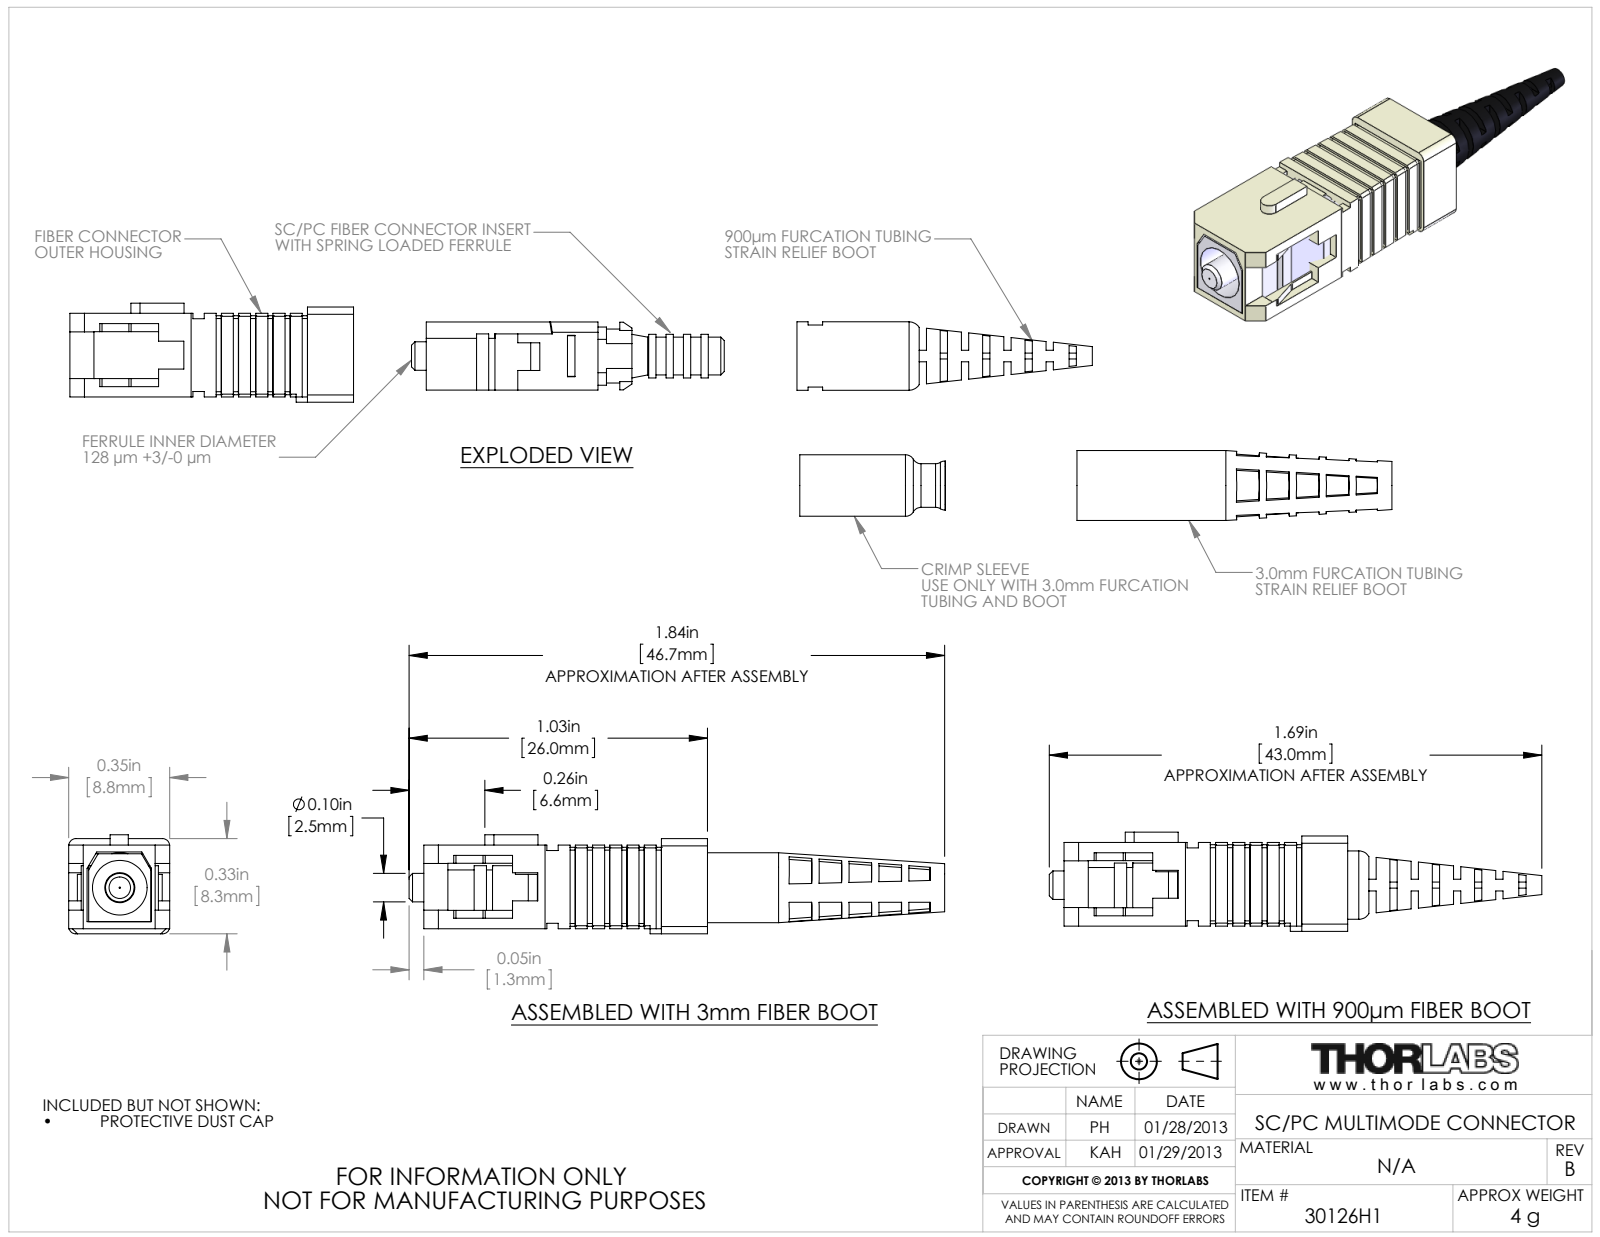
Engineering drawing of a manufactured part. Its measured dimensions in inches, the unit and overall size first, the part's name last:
Units: inches
Overall size (bounding box): 1.693 × 0.347 × 0.341
Round holes (diameter × count): ⌀0.045 ×1, ⌀0.051 ×1, ⌀0.101 ×1, ⌀0.103 ×1, ⌀0.125 ×1, ⌀0.143 ×1, ⌀0.169 ×1, ⌀0.175 ×1, ⌀0.183 ×1, ⌀0.186 ×1, ⌀0.188 ×1
Round bosses / shafts (diameter × count): ⌀0.235 ×1, ⌀0.2 ×1, ⌀0.15 ×1, ⌀0.13 ×1, ⌀0.112 ×1, ⌀0.098 ×1, ⌀0.09 ×1
Partial cylindrical surfaces — rounded edges, fillets, slot ends (radius × count): R0.025 ×8, R0.035 ×3, R0.126 ×2, R0.031 ×1, R0.091 ×1, R0.092 ×1
Main face-to-face distances: 0.264, 0.024, 0.287, 0.042, 0.023, 0.04, 0.307, 0.306, 0.244, 0.256
Volume: 0.076 in³ · Surface area: 5.573 in²
Bodies: 5 solids, 541 faces (440 planar, 81 cylindrical, 20 other)
Part name (STEP PRODUCT): 2337-E0W
STEP written by: SolidWorks 2011 (AUTOMOTIVE_DESIGN)
